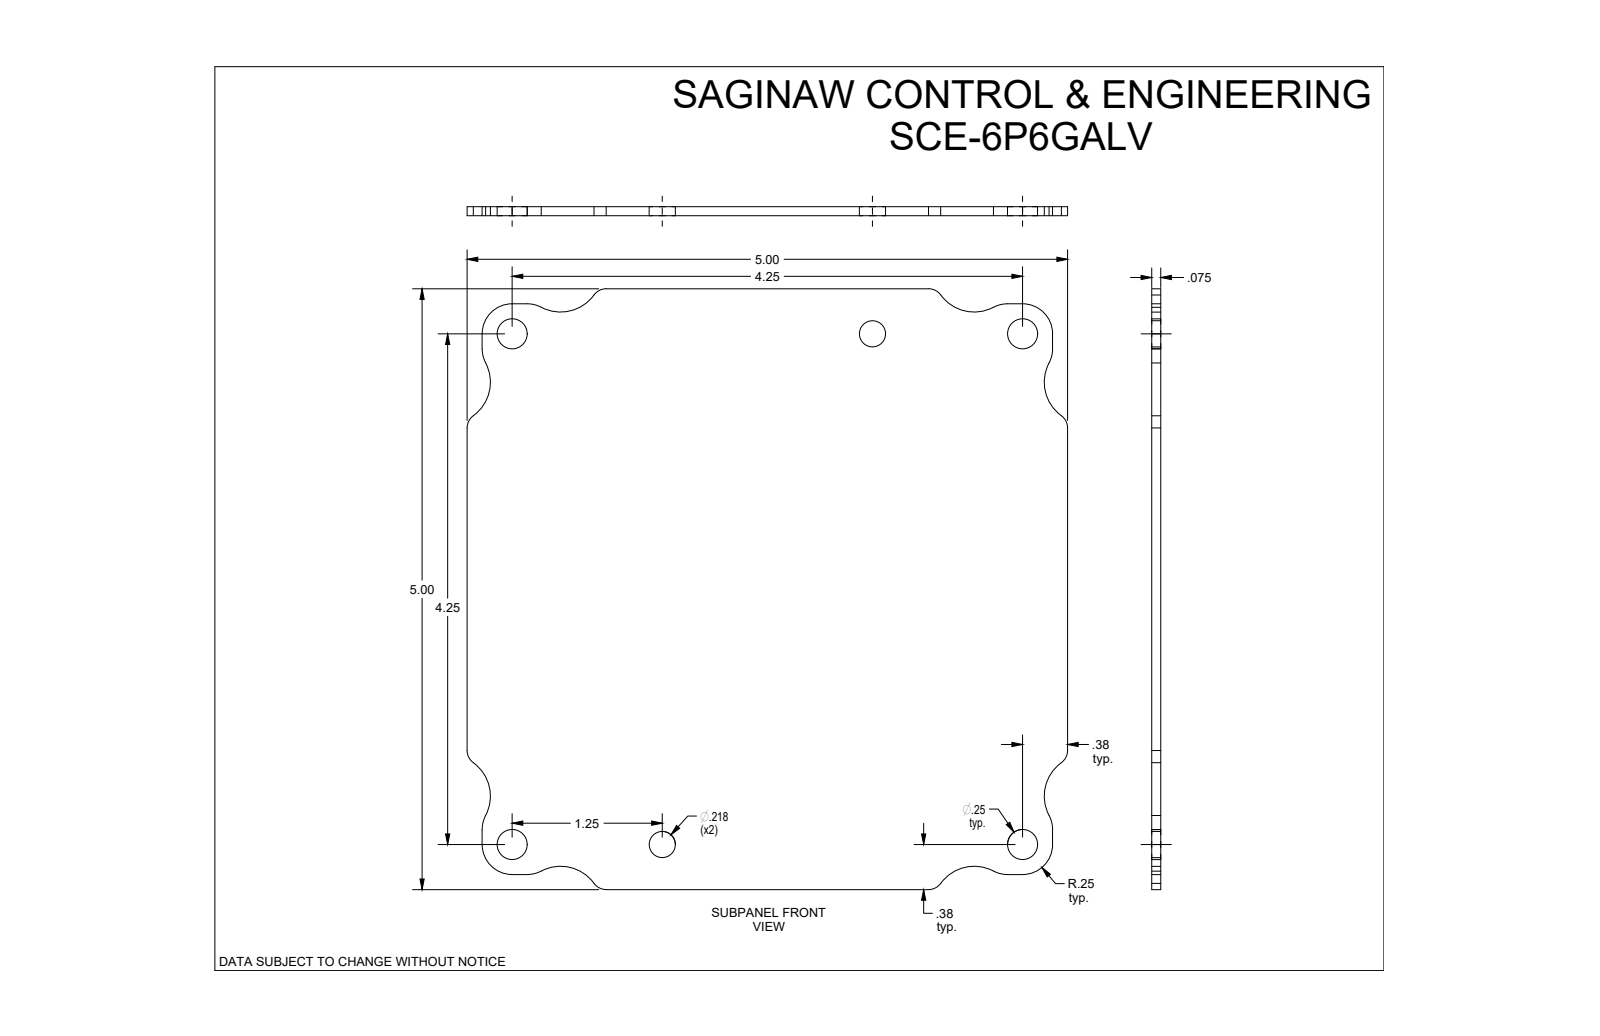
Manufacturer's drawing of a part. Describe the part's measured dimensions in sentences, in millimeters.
The part is named "SCE-6P6GALV". Its 3-D file was written by "SolidWorks 2019 (CONFIG_CONTROL_DESIGN)". It is 1 solid with 48 faces: 14 planar, 34 cylindrical and 0 other. Overall it measures 127 by 127 by 1.9 millimeters. Its volume is 28 920 cubic millimeters and its surface area 31 500 square millimeters. Round holes: 4 of diameter 6.4, 2 of diameter 5.5. Partial cylindrical surfaces (rounded edges, fillets, slot ends): 12 of radius 6.4, 8 of radius 3.2, 8 of radius 8.7. The main face-to-face distances are 1.9, 127, 3.2, 123.8, 120.7. The hole center spacings are 108, 31.8, 76.2, 112.5, 132.1, 152.7, 116.7.
